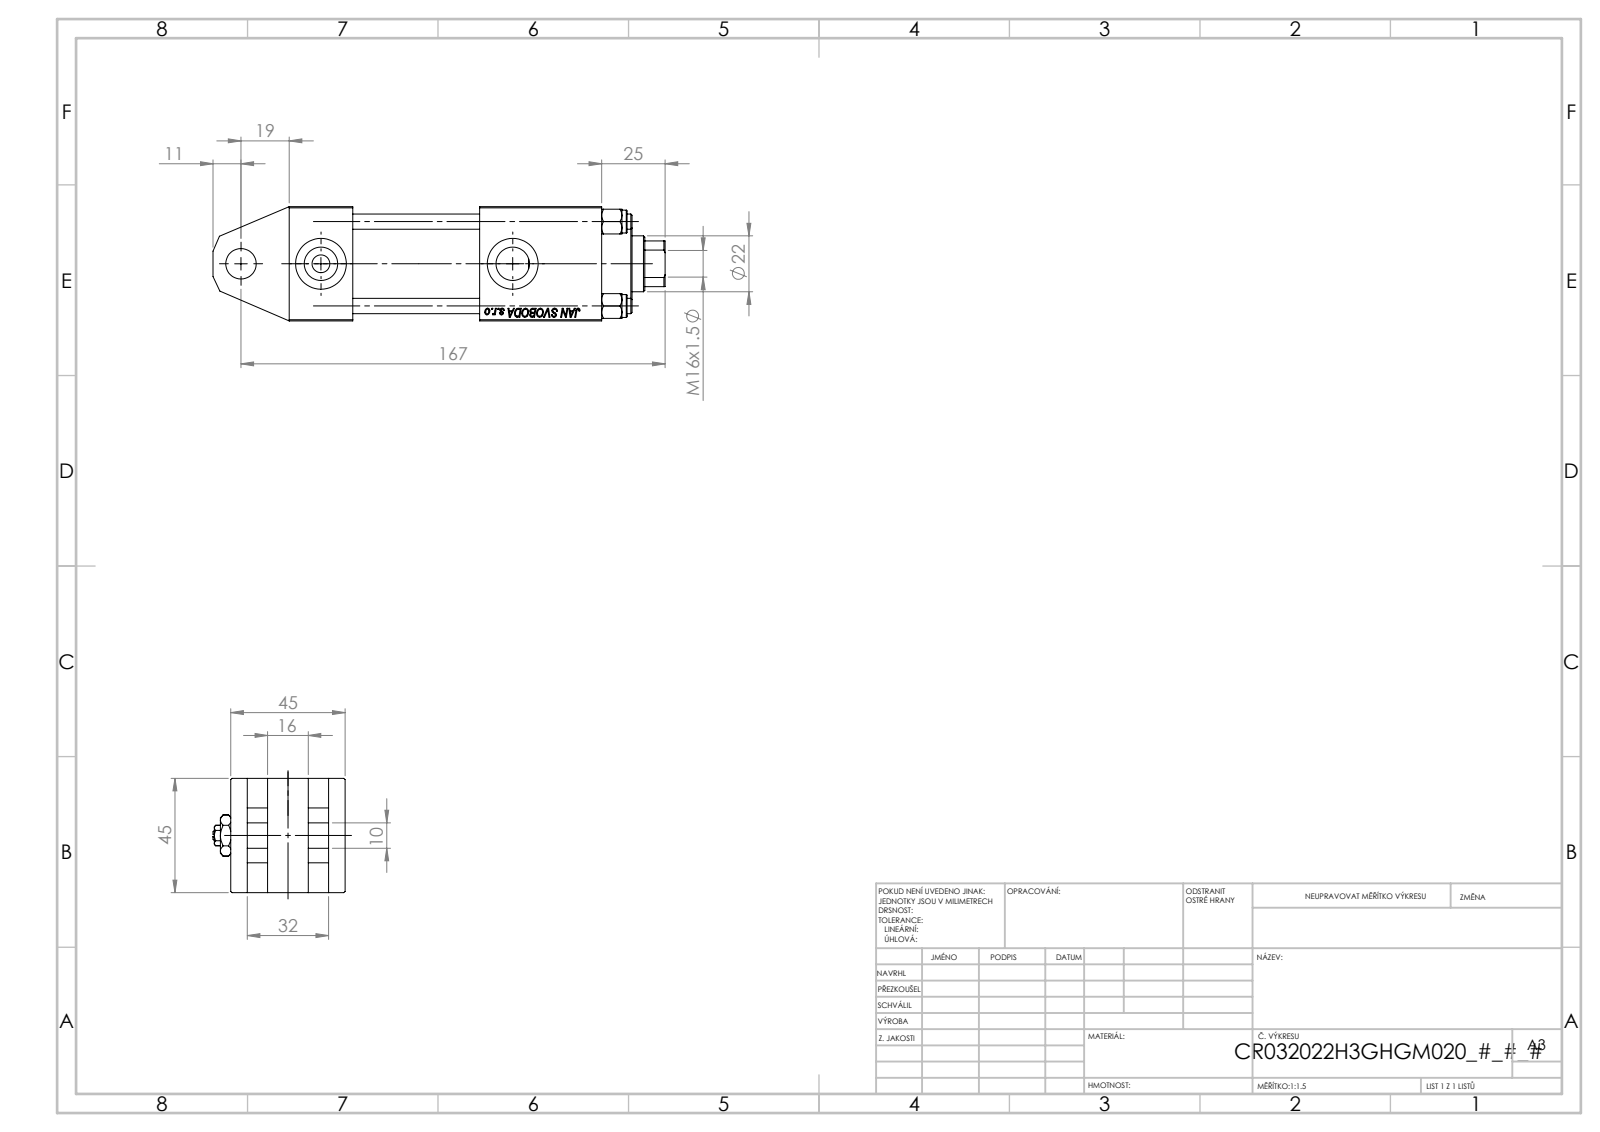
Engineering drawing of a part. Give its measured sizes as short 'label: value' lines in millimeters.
name: V215_VC_A; V215CR_TYCINKA_H; NUT_M5_H; Zatka_pro_OIL_PORT (+2 more)
written by: SolidWorks 2019 (CONFIG_CONTROL_DESIGN)
unit: mm
bodies: 13 solids, 1236 faces (564 planar, 98 cylindrical, 574 other)
size: 178 × 52 × 45
volume: 223 189 mm³; area: 80 411 mm²
holes: 4× ⌀6, 2× ⌀2.5, 2× ⌀7, 2× ⌀13.16, 2× ⌀20, 1× ⌀10.5, 1× ⌀12, 1× ⌀22, 1× ⌀24, 1× ⌀25, 1× ⌀32, 1× ⌀33
bosses: 4× ⌀9, 1× ⌀38, 1× ⌀34
rounds: 1× R10.5
face distances: 45, 8, 6.5, 38.5, 24, 14.5, 30.5, 25, 123, 50
hole spacings: 16.7, 23.48, 33.2, 35.47, 14.75, 46.95, 29.5, 31.5
